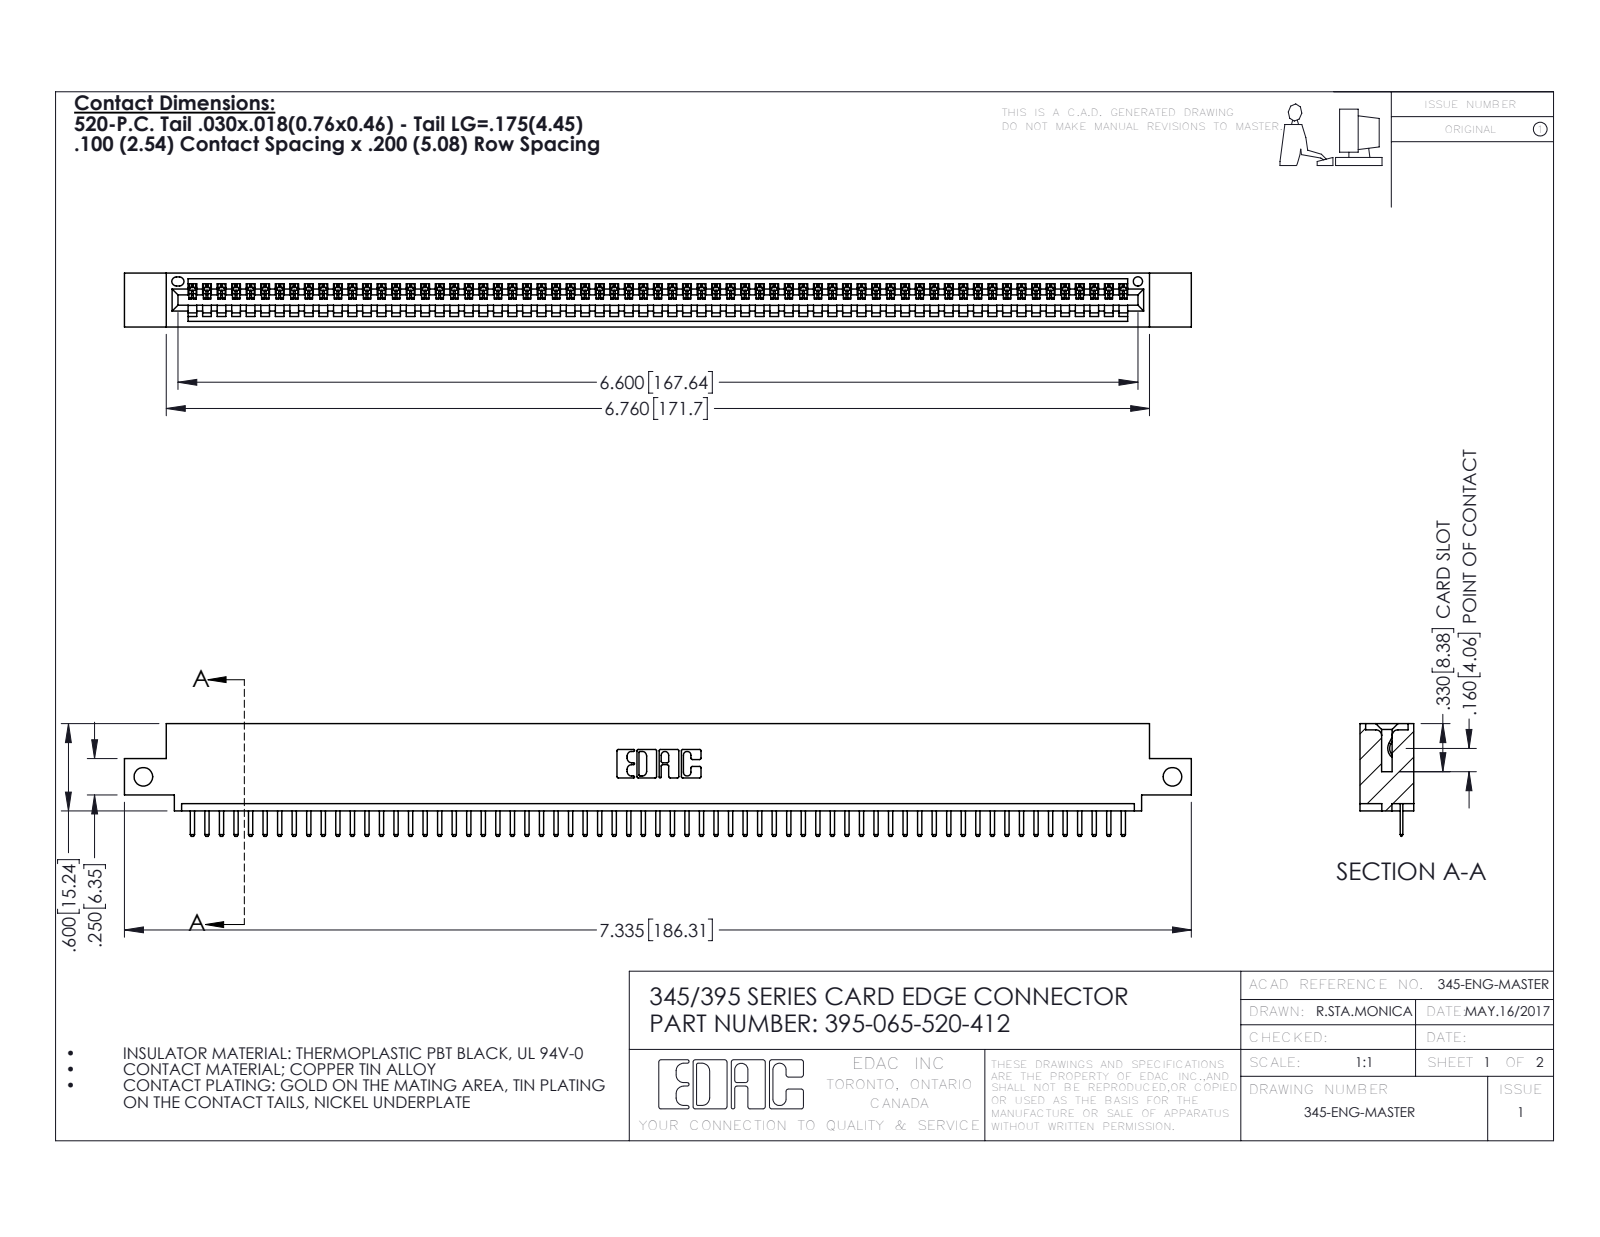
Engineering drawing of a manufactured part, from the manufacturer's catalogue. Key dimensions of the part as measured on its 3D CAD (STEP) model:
Part name (STEP PRODUCT): 395-065-520-412; 345 Part_0.110 Offset - Side Mount; 345-292-001_345-293-120
STEP written by: SolidWorks 2016 (CONFIG_CONTROL_DESIGN)
Units: inches
Bodies: 66 solids, 4160 faces (2814 planar, 1346 cylindrical, 0 other)
Overall size (bounding box): 7.335 × 0.775 × 0.37
Volume: 1.07 in³ · Surface area: 35.57 in²
Round holes (diameter × count): ⌀0.128 ×2, ⌀0.064 ×1
Partial cylindrical surfaces — rounded edges, fillets, slot ends (radius × count): R0.01 ×132, R0.006 ×130, R0.01 ×22, R0.007 ×6, R0.031 ×6, R0.026 ×3, R0.031 ×2, R0.04 ×2
Main face-to-face distances: 0.298, 0.072, 0.37, 0.2, 0.098, 0.272, 0.025, 0.225, 0.072, 0.149
Hole centre spacings: 7.075
